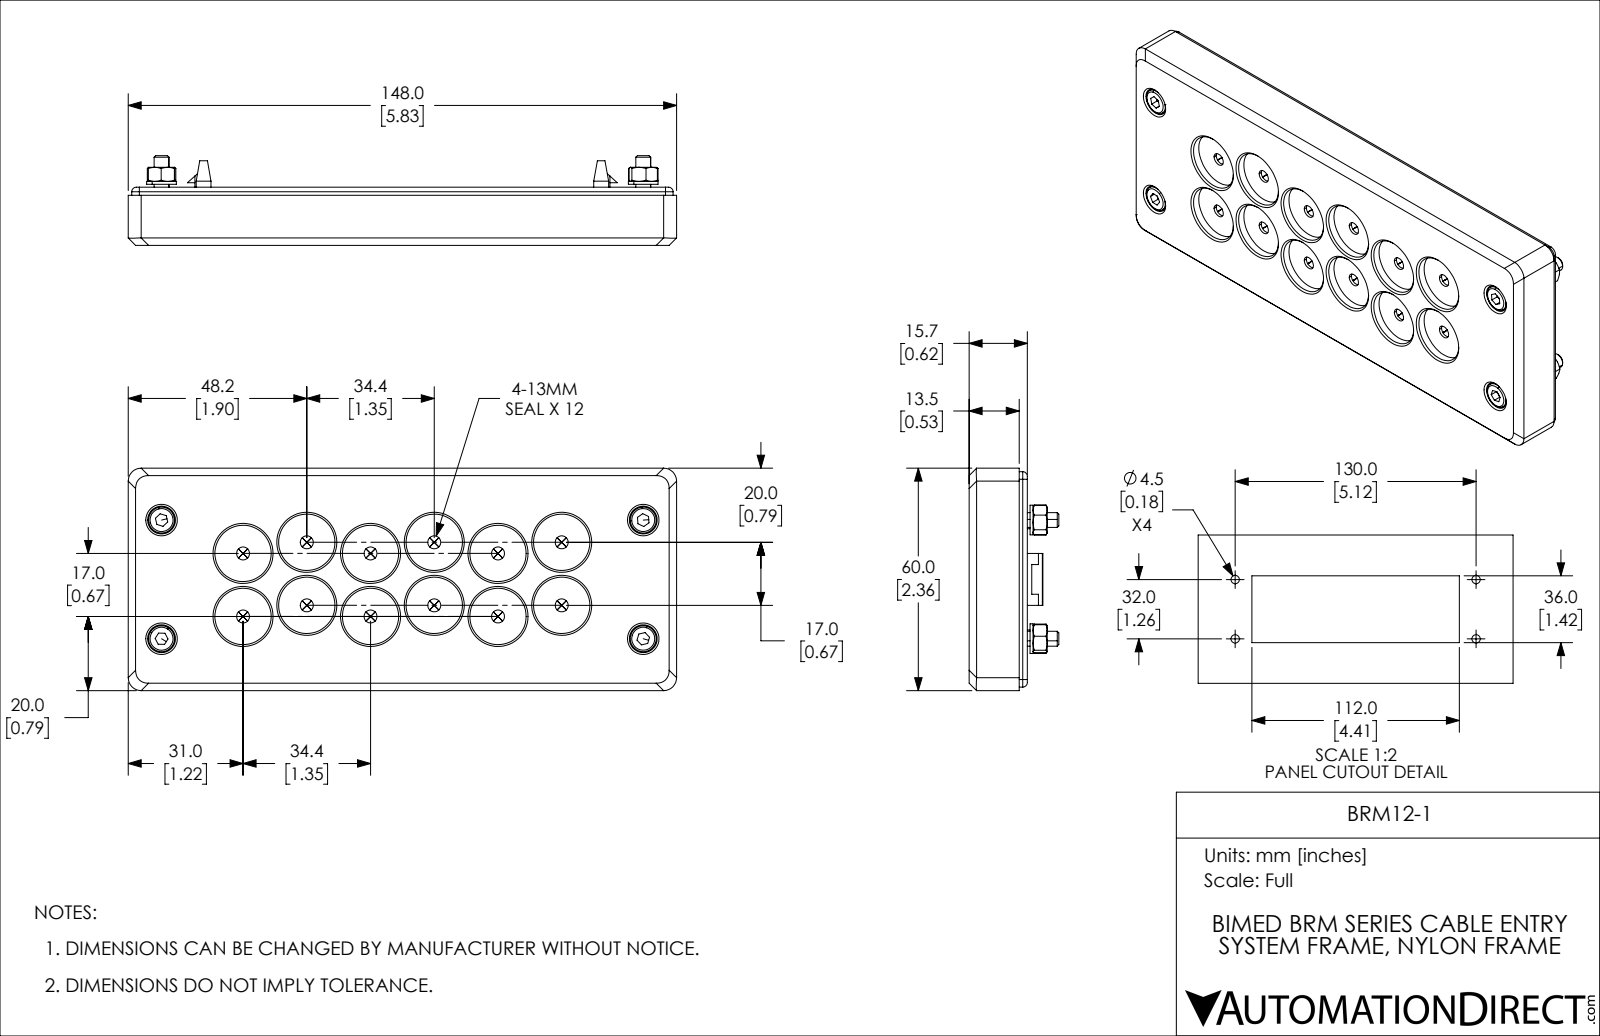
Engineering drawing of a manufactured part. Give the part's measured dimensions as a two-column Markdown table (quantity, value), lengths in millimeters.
| quantity | value |
| --- | --- |
| part name | BRM12-1 |
| STEP written by | SolidWorks 2021 (CONFIG_CONTROL_DESIGN) |
| units | millimeters |
| bodies | 18 solids, 1205 faces (369 planar, 548 cylindrical, 288 other) |
| overall size | 148 × 60 × 24.2 |
| volume | 86 298 mm³ |
| surface area | 86 920 mm² |
| round holes (diameter × count) | 2.8 × 20, 3.5 × 12, 15.2 × 12, 15.5 × 12, 2.5 × 4, 3.24 × 4, 4.3 × 4, 4.5 × 4, 7.5 × 4 |
| round bosses / shafts (diameter × count) | 2.5 × 16, 4 × 8, 8 × 4, 7 × 4 |
| partial cylindrical surfaces (radius × count) | 1 × 28, 8.25 × 12, 1.25 × 8, 5 × 8, 0.5 × 6, 2 × 4, 2.05 × 4, 3.5 × 4 |
| main face-to-face distances | 0.8, 2, 2.8, 3, 5, 5.8, 2.5, 3.3, 8.3, 5.3 |
| hole center spacings | 17.46, 34.4, 38.37, 17, 51.69, 22.18, 26.38, 11.36 |
